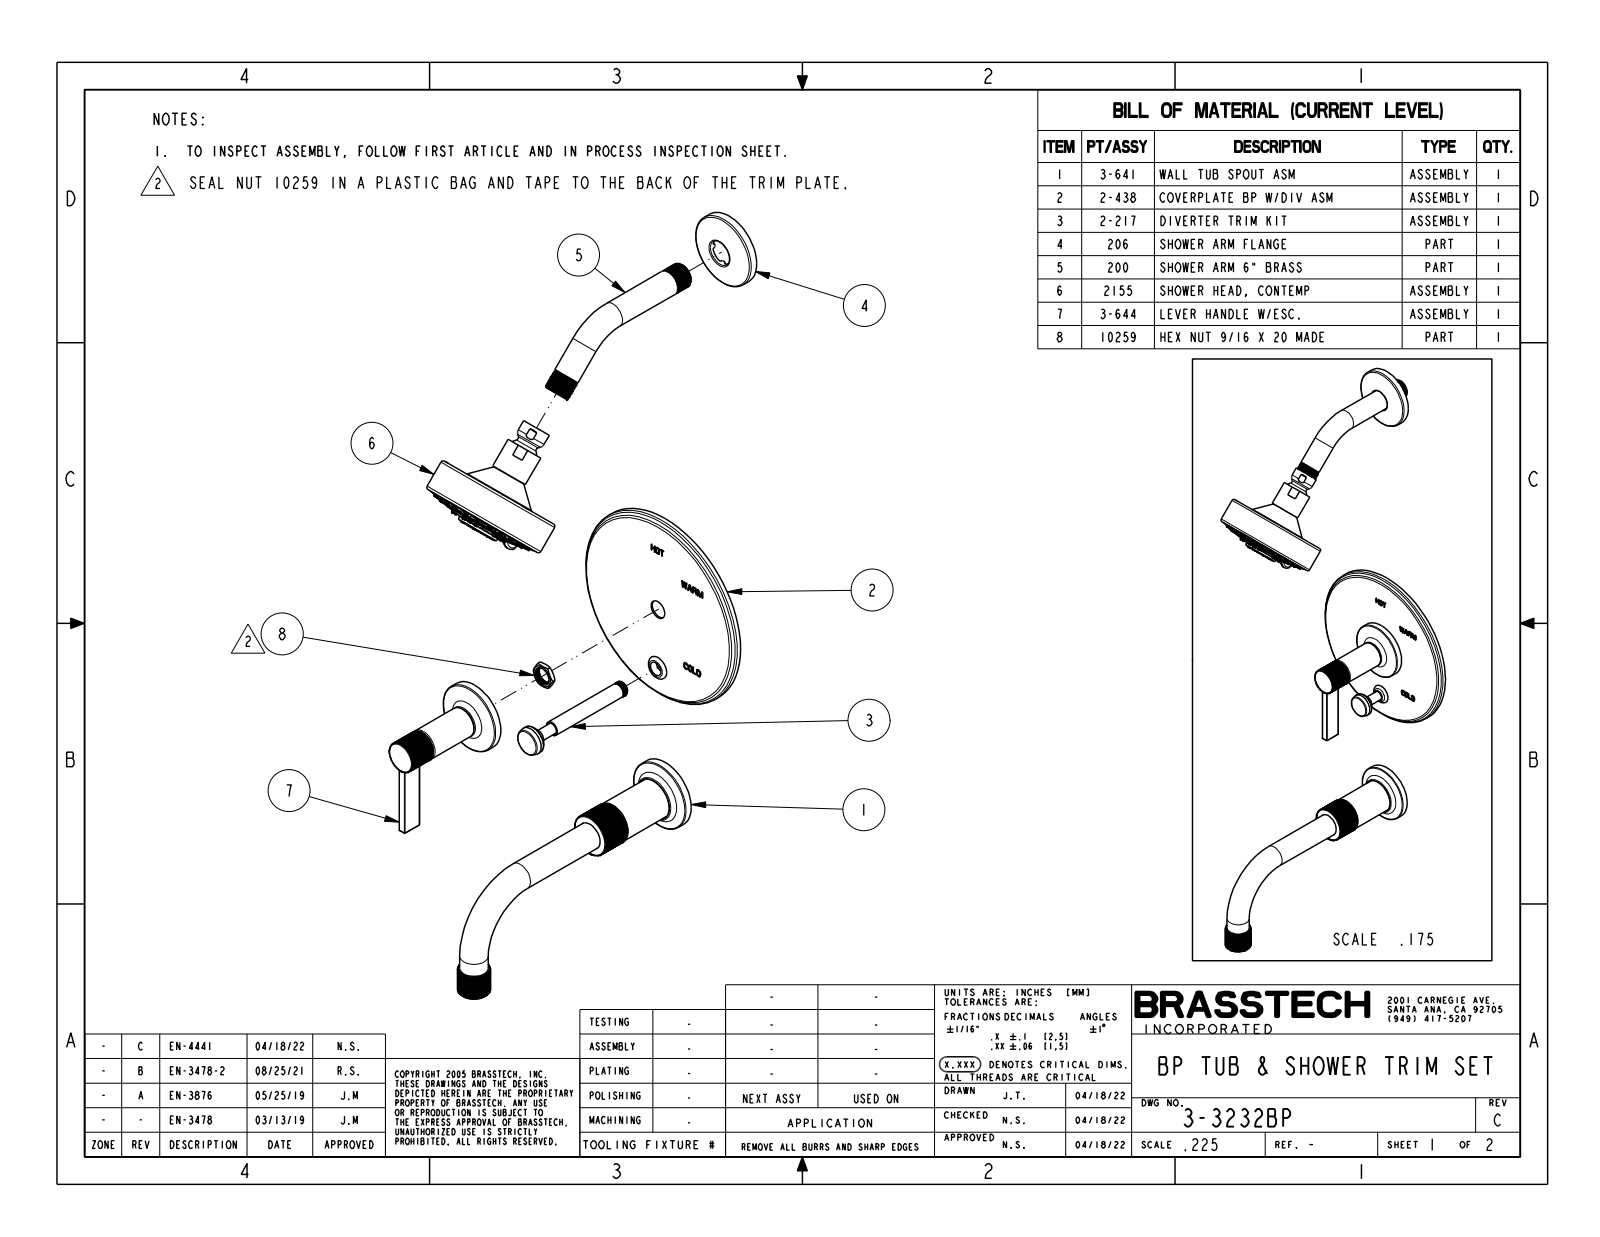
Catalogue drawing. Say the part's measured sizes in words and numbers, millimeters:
The part is named "13145; 13150; 11670; 20-422_ASM (+8 more)". Its 3-D file was written by "CREO PARAMETRIC BY PTC INC, 2018400 (CONFIG_CONTROL_DESIGN)". It is 71 solids with 9705 faces: 4427 planar, 2621 cylindrical and 2657 other. Overall it measures 595.6 by 286.7 by 165.1 millimeters. Its volume is 340 500 cubic millimeters and its surface area 493 800 square millimeters. Round holes: 32 of diameter 1.1, 15 of diameter 2.5, 12 of diameter 1.5, 8 of diameter 2, 8 of diameter 2.4, 8 of diameter 4.7, 7 of diameter 3, 3 of diameter 3.8, 3 of diameter 6.4, 3 of diameter 7, 2 of diameter 2.8, 2 of diameter 3.8. Round bosses or shafts: 39 of diameter 3.6, 23 of diameter 4.2, 3 of diameter 8, 3 of diameter 6.2, 2 of diameter 57.2, 2 of diameter 46, 2 of diameter 25.4, 2 of diameter 22.2. Partial cylindrical surfaces (rounded edges, fillets, slot ends): 52 of radius 0.5, 29 of radius 0.3, 15 of radius 2.1, 14 of radius 0.2, 12 of radius 0.5, 12 of radius 0.8, 9 of radius 2, 8 of radius 2.2. The main face-to-face distances are 1.3, 2.5, 5.3, 17.7, 16.7, 1, 11.4, 12.4, 7.8, 19.2. The hole center spacings are 9.6, 10.7, 7, 5.3, 7, 9.4, 10.7, 15.4.
